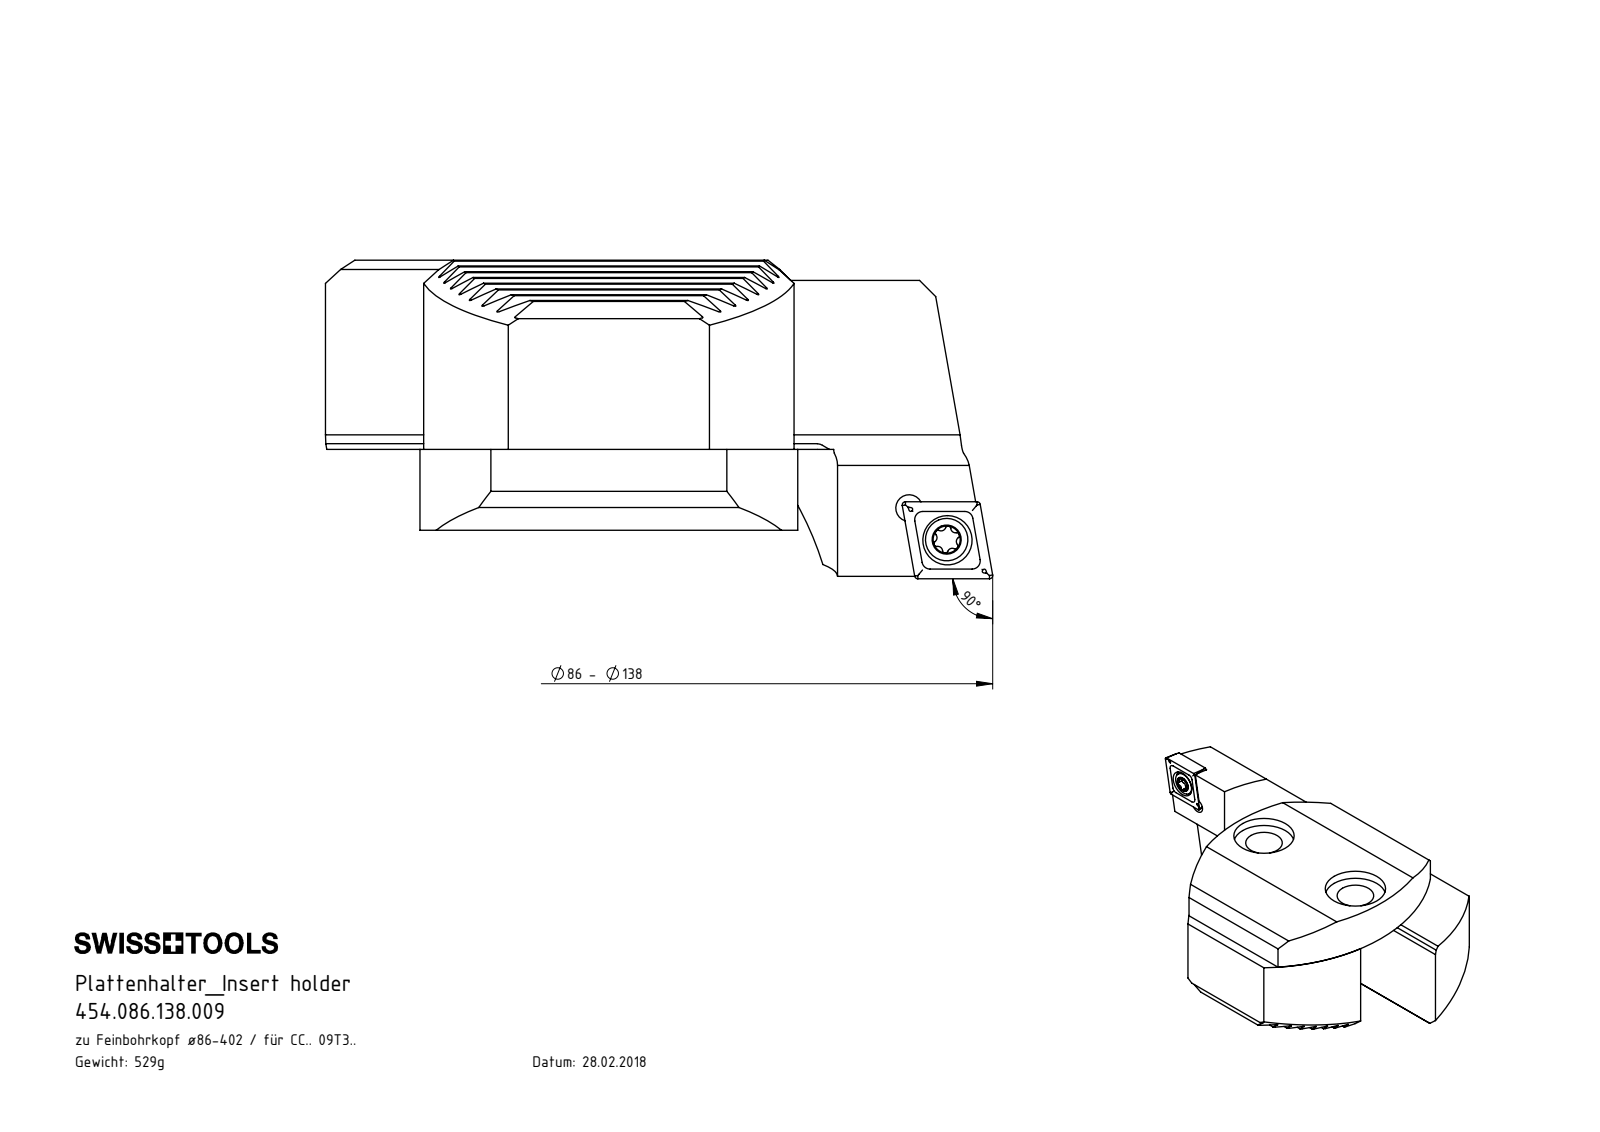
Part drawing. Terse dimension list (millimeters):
name: F00-WCB.086.001_C; F00-WCB.086.000; F00-WCB.086.003_A; WCB-ER2.001.009_A (+3 more)
written by: SolidWorks 2017 (CONFIG_CONTROL_DESIGN)
unit: mm
bodies: 5 solids, 442 faces (264 planar, 59 cylindrical, 119 other)
size: 82.57 × 55 × 39.4
volume: 67 401 mm³; area: 19 323 mm²
holes: 2× ⌀3.3, 2× ⌀8.5, 2× ⌀14, 1× ⌀4.4, 1× ⌀6.1
bosses: 1× ⌀5.25, 1× ⌀4
rounds: 16× R0.2, 7× R40, 6× R0.34, 6× R0.59, 1× R0.8
face distances: 2.38, 21.3, 33.7, 4.76, 12.4, 10, 7.15, 9.53, 11.91, 7.14
hole spacings: 6.07, 6.2, 30
